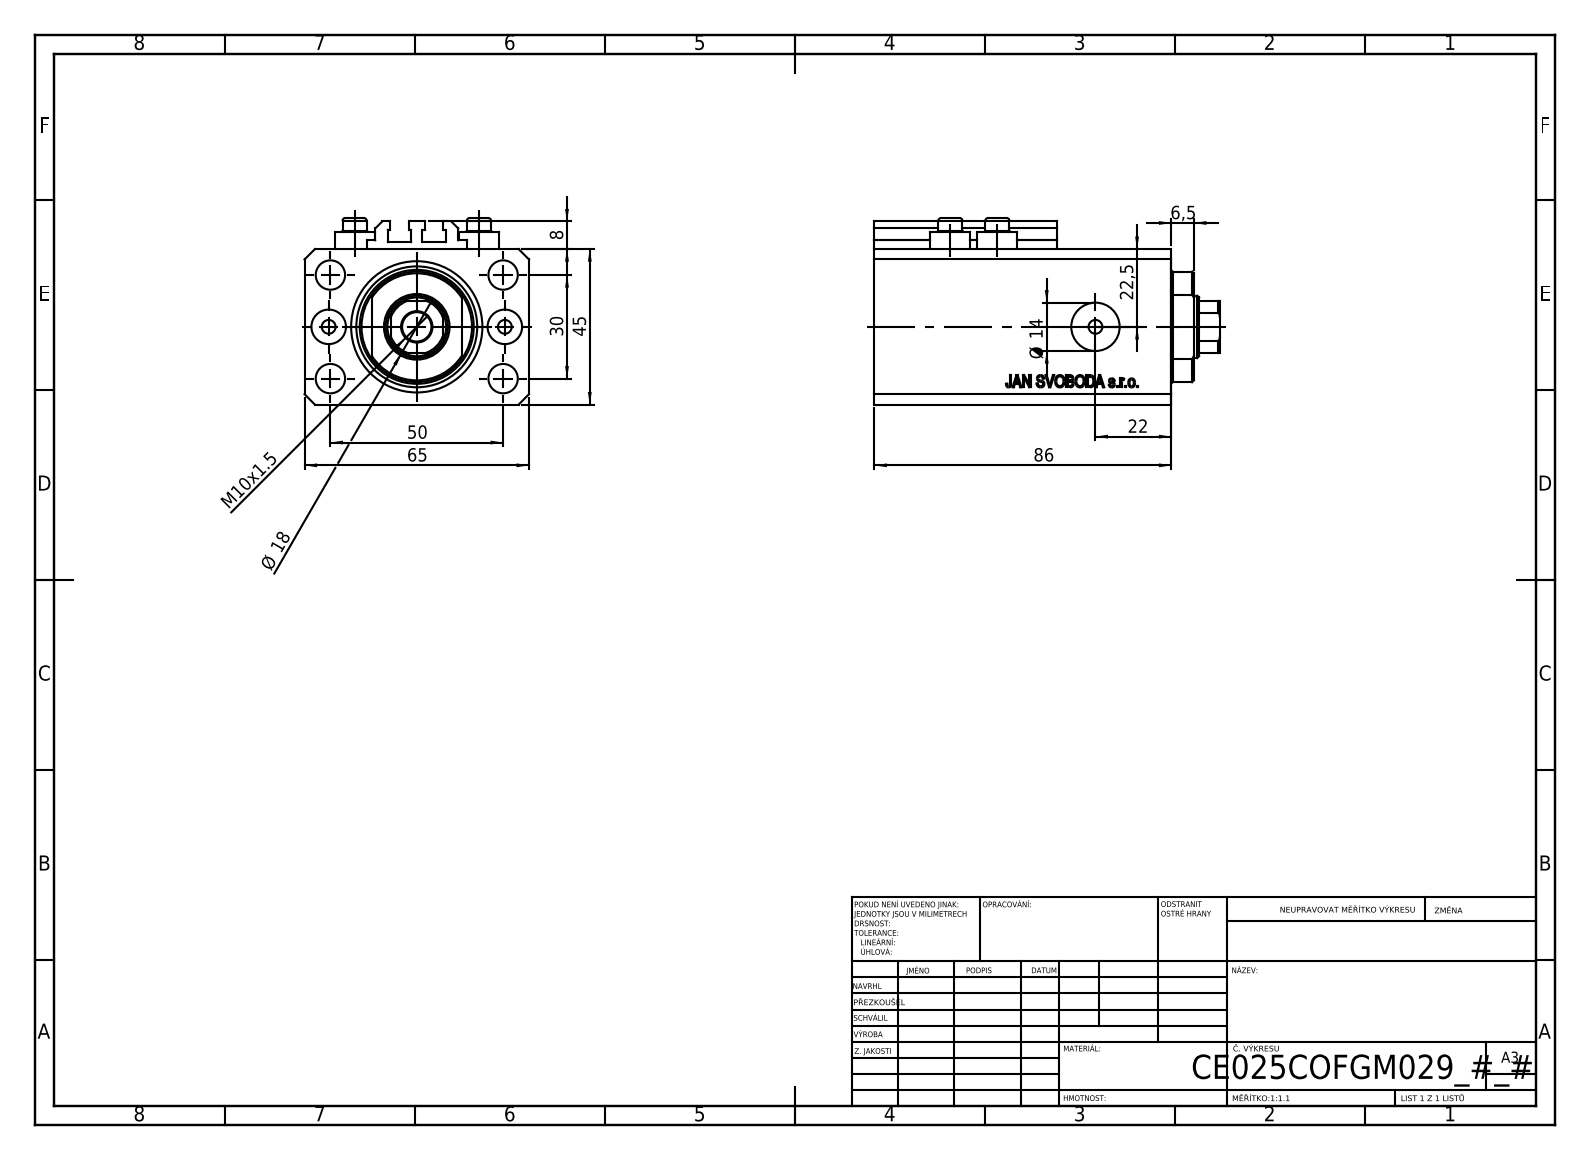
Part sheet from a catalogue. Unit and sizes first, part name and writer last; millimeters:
Units: millimetres
Overall size (bounding box): 100 × 65 × 54
Round holes (diameter × count): ⌀4 ×8, ⌀8.5 ×5, ⌀10 ×2, ⌀14 ×2, ⌀18 ×1, ⌀25 ×1, ⌀38 ×1
Round bosses / shafts (diameter × count): ⌀11.6 ×4, ⌀7 ×4
Partial cylindrical surfaces — rounded edges, fillets, slot ends (radius × count): R0.2 ×10, R8.5 ×1, R16 ×1
Main face-to-face distances: 45, 65, 14, 72, 86, 47, 6.9, 65.1, 79.1, 3
Hole centre spacings: 15.01, 29.15, 52.68, 13.6, 25.5, 30, 36, 38.48
Volume: 235 067 mm³ · Surface area: 62 267 mm²
Bodies: 8 solids, 1034 faces (504 planar, 86 cylindrical, 444 other)
Part name (STEP PRODUCT): V250CE_VC_C; V250CE_C_VCP; V250CE_C_Body; ALLEN BOLT V250CE
STEP written by: SolidWorks 2019 (CONFIG_CONTROL_DESIGN)
